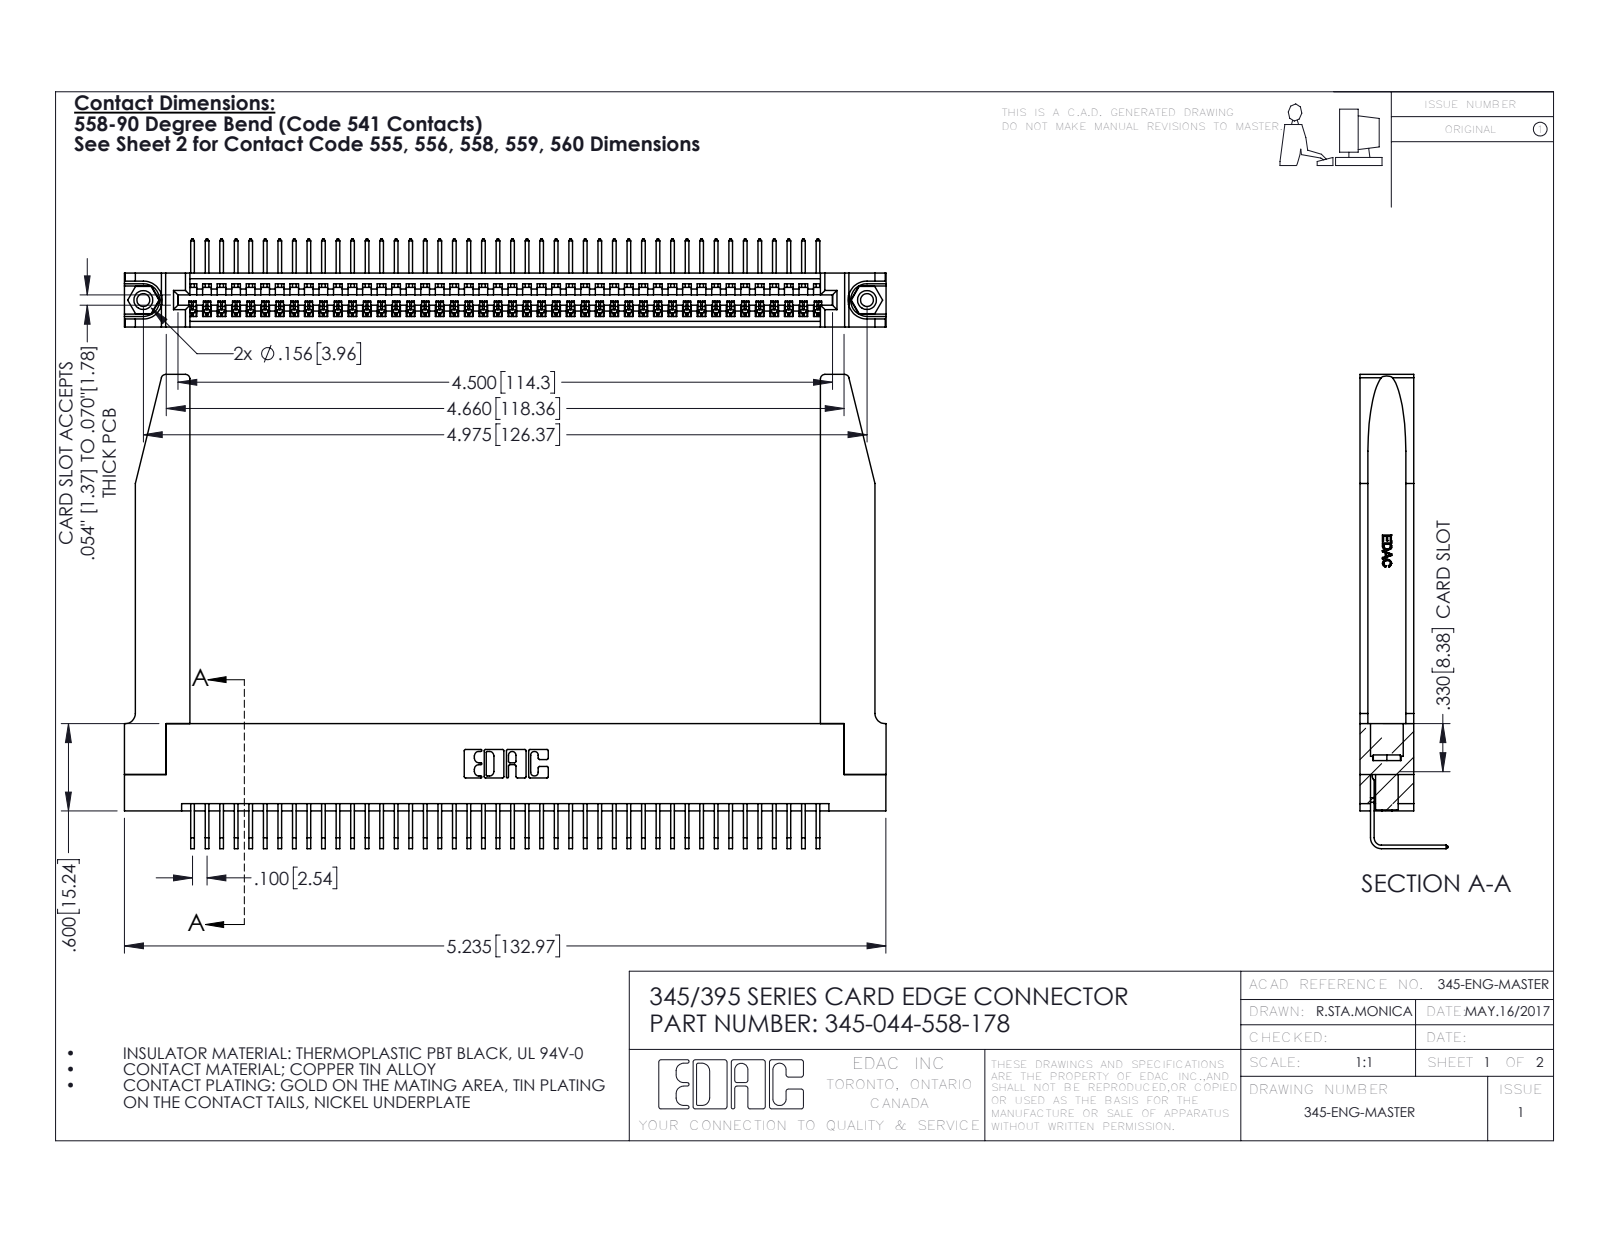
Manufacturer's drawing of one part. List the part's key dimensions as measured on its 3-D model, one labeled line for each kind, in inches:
Part name (STEP PRODUCT): 345 Part_Flush Mounting Lugs - 0.156 Dia-TH; 345-220-078_345-220-078; 345-292-001_558 Tail - 2; 345-044-558-178 (+1 more)
STEP written by: SolidWorks 2016 (CONFIG_CONTROL_DESIGN)
Units: inches
Bodies: 49 solids, 3000 faces (2070 planar, 878 cylindrical, 52 other)
Overall size (bounding box): 5.236 × 3.259 × 0.605
Volume: 1.255 in³ · Surface area: 38.34 in²
Round holes (diameter × count): ⌀0.089 ×2, ⌀0.125 ×2, ⌀0.156 ×2, ⌀0.064 ×1
Round bosses / shafts (diameter × count): ⌀0.155 ×2
Partial cylindrical surfaces — rounded edges, fillets, slot ends (radius × count): R0.006 ×88, R0.01 ×22, R0.03 ×8, R0.007 ×6, R0.031 ×6, R0.026 ×3, R0.031 ×2, R0.04 ×2
Main face-to-face distances: 0.37, 0.072, 0.298, 0.2, 0.098, 0.272, 0.025, 0.225, 0.148, 0.15
Hole centre spacings: 0.27, 4.739, 4.975
